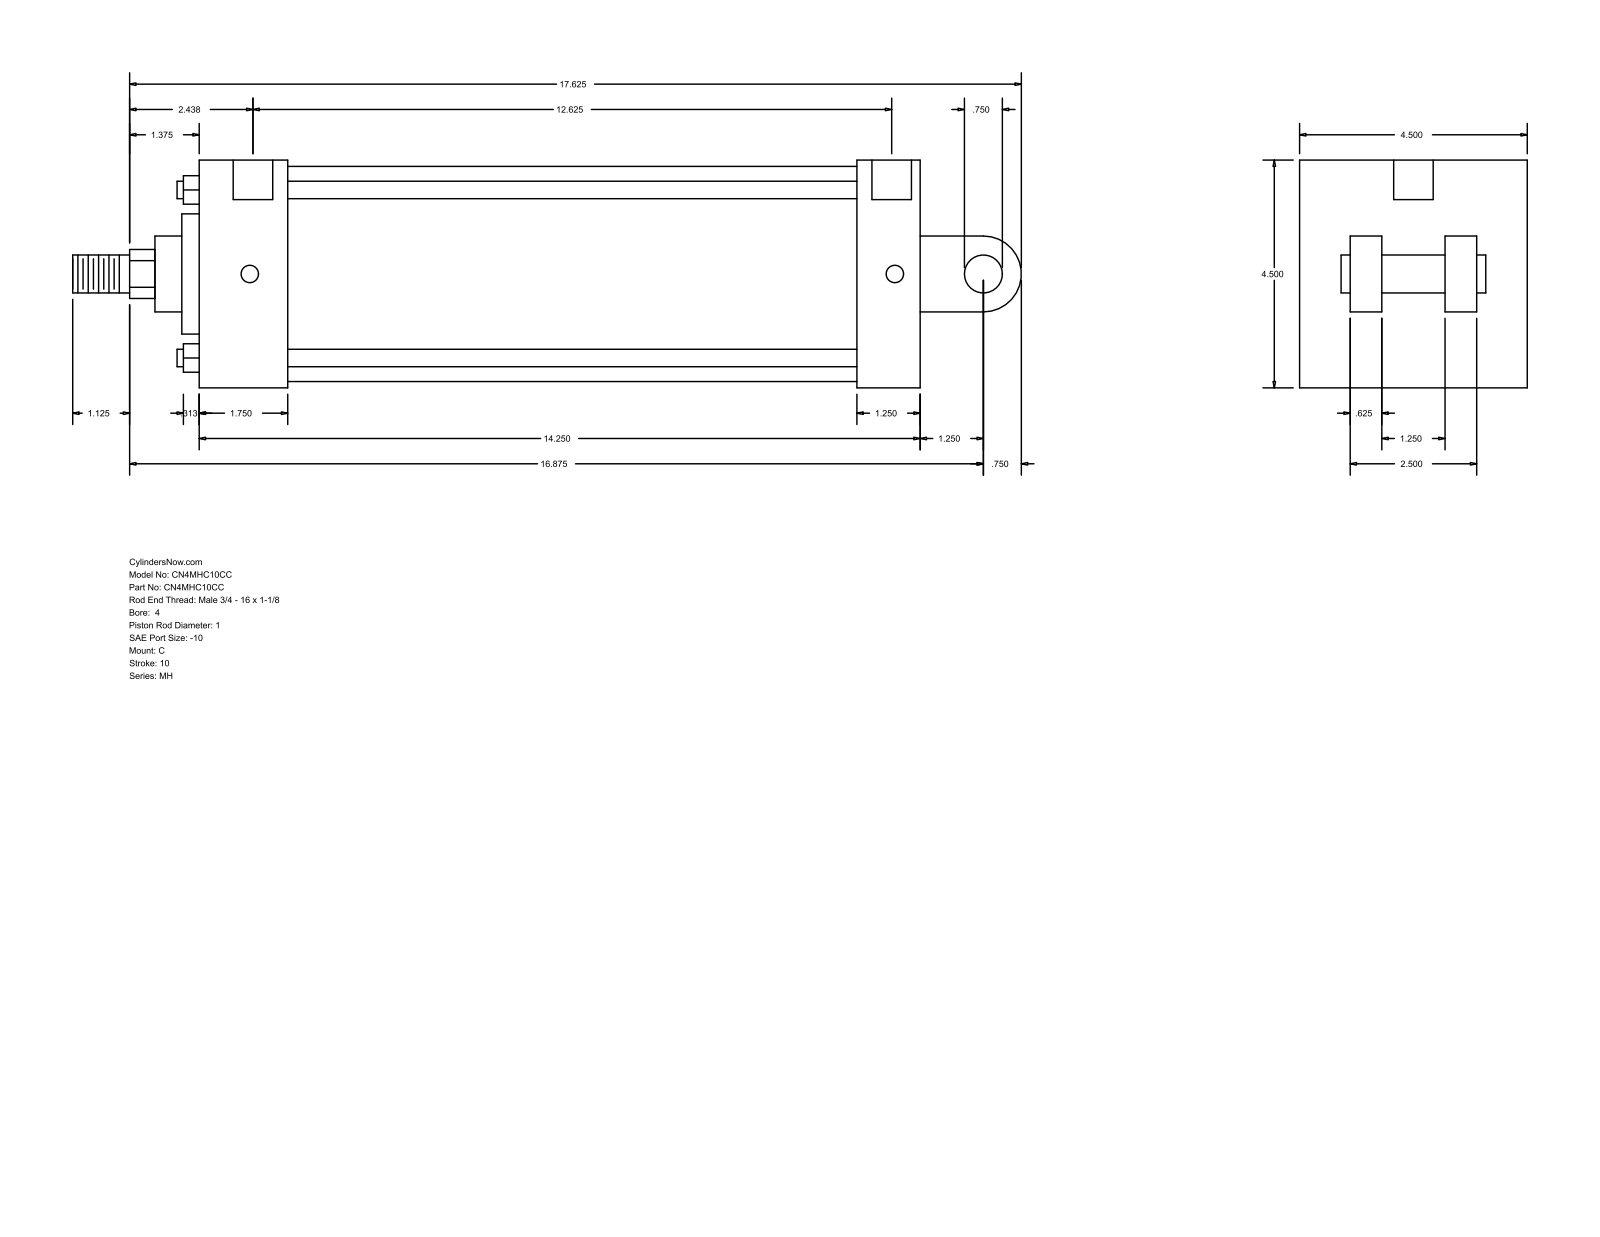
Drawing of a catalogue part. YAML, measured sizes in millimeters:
part_name: "MH_C__0400_1"
step_written_by: "GSSL Pune (CONFIG_CONTROL_DESIGN)"
units: millimeters
bodies: {solids: 0, faces: 101, planar: 71, cylindrical: 30, other: 0}
overall_size: [476.25, 114.3, 114.3]
round_holes:
  - {diameter: 8.73, count: 4}
  - {diameter: 19.84, count: 2}
round_bosses_or_shafts:
  - {diameter: 8.76, count: 4}
  - {diameter: 19.05, count: 2}
  - {diameter: 107.95, count: 1}
  - {diameter: 60.33, count: 1}
  - {diameter: 38.1, count: 1}
  - {diameter: 25.4, count: 1}
partial_cylinders:
  - {radius: 12.29, count: 1}
  - {radius: 19.05, count: 1}
face_to_face_distances: [114.3, 361.96, 31.76, 44.46, 330.2, 285.74, 317.5, 73.03, 41.27, 38.1]
hole_center_spacings: [323.85, 1.58, 1.59, 320.68, 322.26, 322.27]
